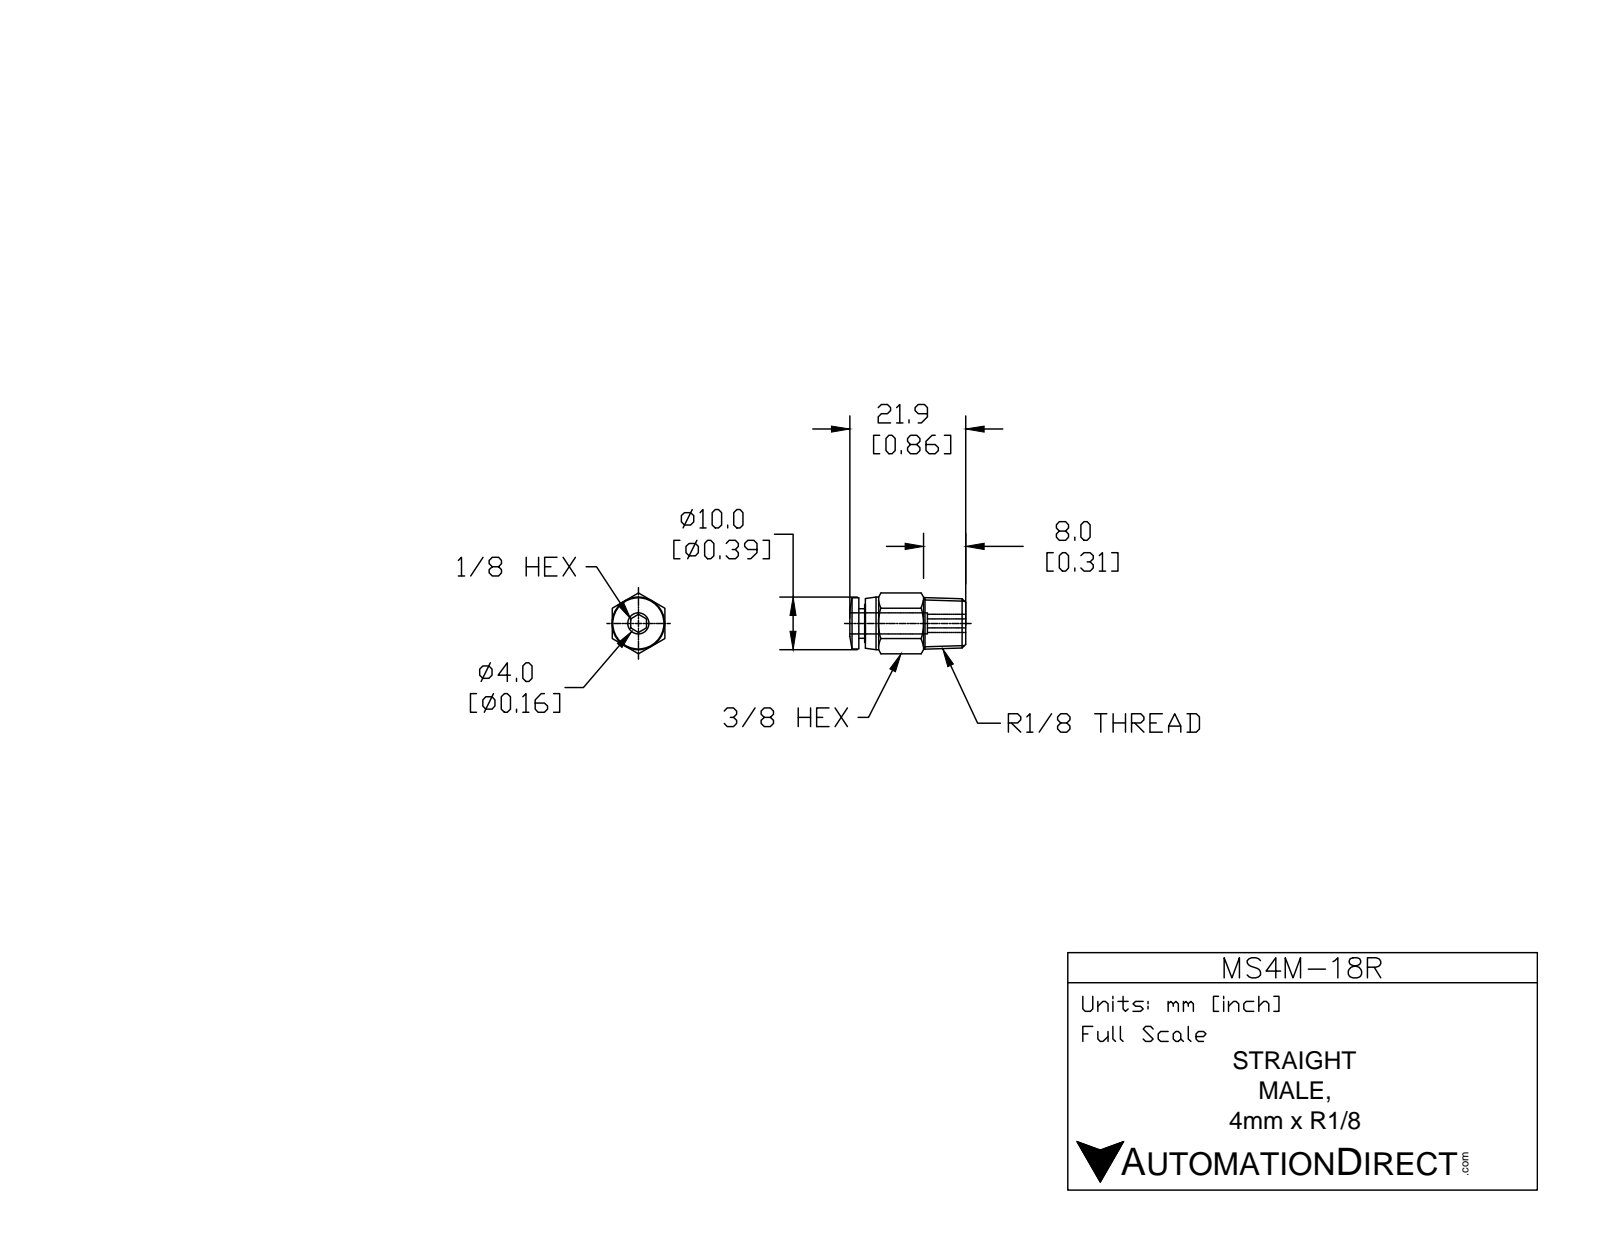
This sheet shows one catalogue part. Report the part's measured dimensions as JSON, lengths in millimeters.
{"part_name": "MS4M-18R", "step_written_by": "SolidWorks 2015 (AUTOMOTIVE_DESIGN)", "units": "millimeters", "bodies": {"solids": 1, "faces": 49, "planar": 13, "cylindrical": 12, "other": 24}, "overall_size": [21.9, 11.6, 10], "volume_mm3": 1300, "surface_area_mm2": 1167, "round_holes": [[3.5, 1], [4.3, 1]], "round_bosses_or_shafts": [[10, 1], [9.7, 1], [7.2, 1], [5.6, 1]], "face_to_face_distances": [10, 20.2, 19, 1.2, 19.2, 1.1, 7.2, 11.8, 11.9, 13]}
